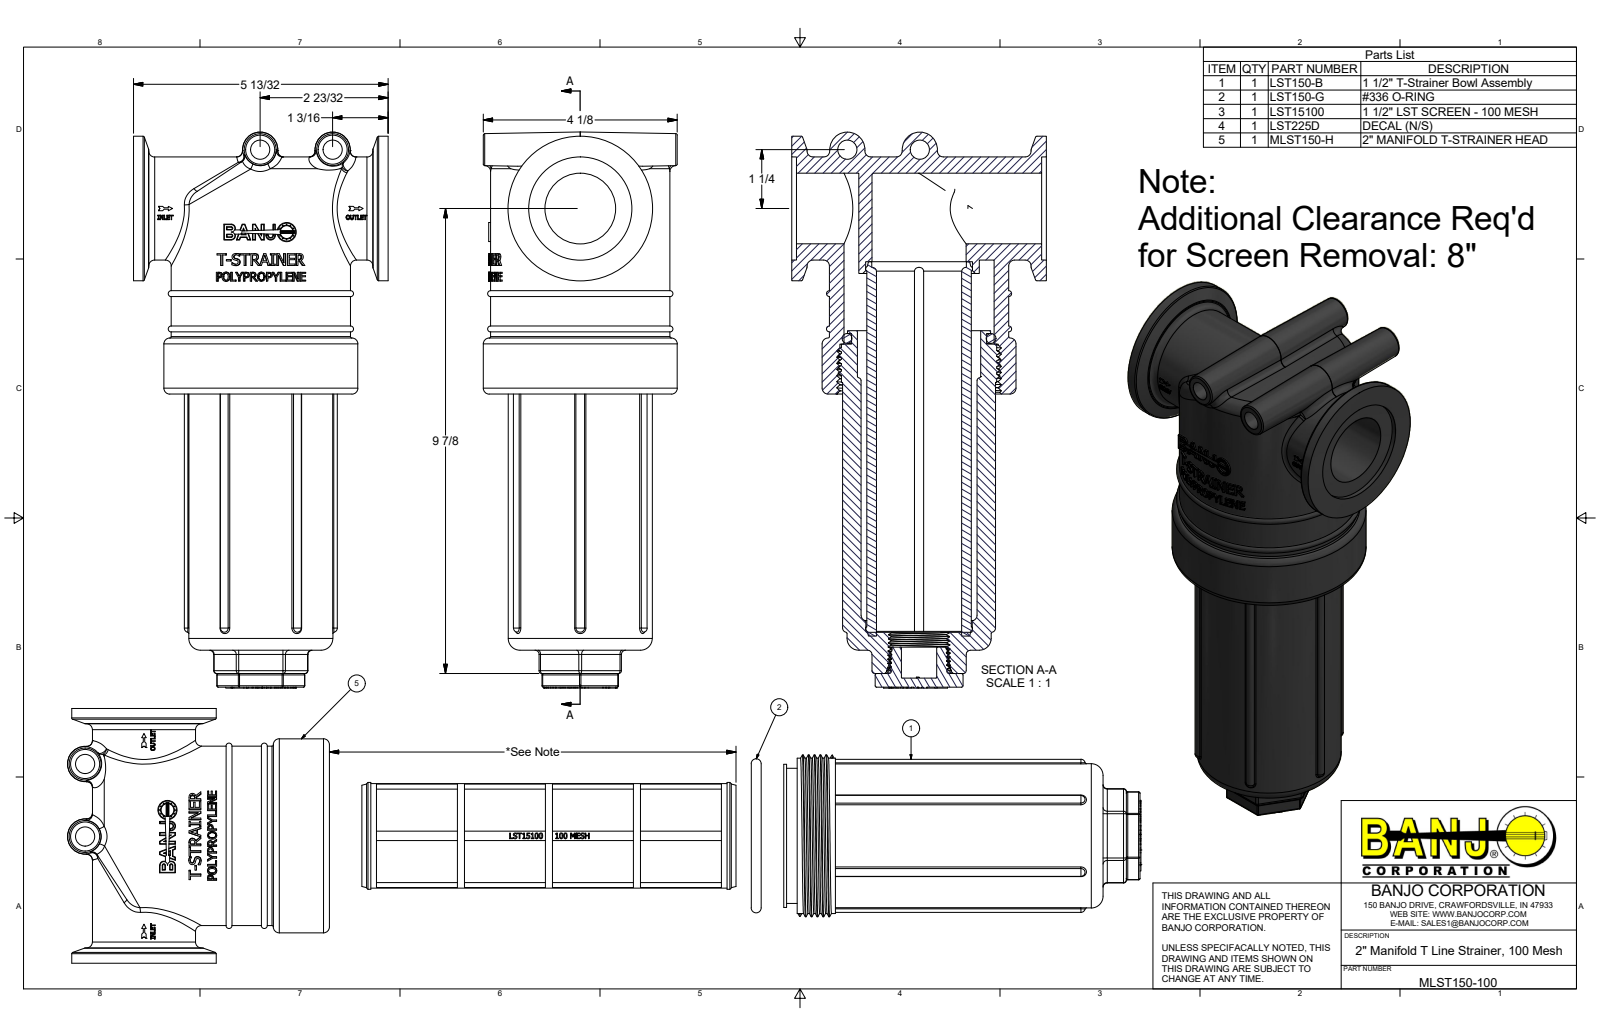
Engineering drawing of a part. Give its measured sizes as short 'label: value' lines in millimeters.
name: MLST150-H; LST150-XB; LSQ200-R; LSQ200-PL (+4 more)
written by: Autodesk Inventor 2014 (AUTOMOTIVE_DESIGN)
unit: mm
bodies: 30 solids, 1875 faces (987 planar, 255 cylindrical, 633 other)
size: 299.97 × 138.18 × 104.65
volume: 841 795 mm³; area: 323 932 mm²
holes: 2× ⌀10.32, 1× ⌀6.92, 1× ⌀9.77, 1× ⌀19.05, 1× ⌀38.1, 1× ⌀45.97, 1× ⌀50.04, 1× ⌀50.8, 1× ⌀57.4, 1× ⌀66.55, 1× ⌀81.03, 1× ⌀85.46
bosses: 1× ⌀104.65, 1× ⌀87.26, 1× ⌀83.82, 1× ⌀77.98, 1× ⌀77.79, 1× ⌀77.22, 1× ⌀72.9, 1× ⌀65.02
rounds: 42× R0.76, 13× R1.52, 6× R1.98, 6× R2.29, 6× R2.38, 5× R2.54, 2× R0.6, 2× R0.86
face distances: 2.54, 135.64, 138.18, 31.49, 92.2, 23.37, 155.45, 247.65, 66.55, 71.63
hole spacings: 39.11, 46.81, 50.73
